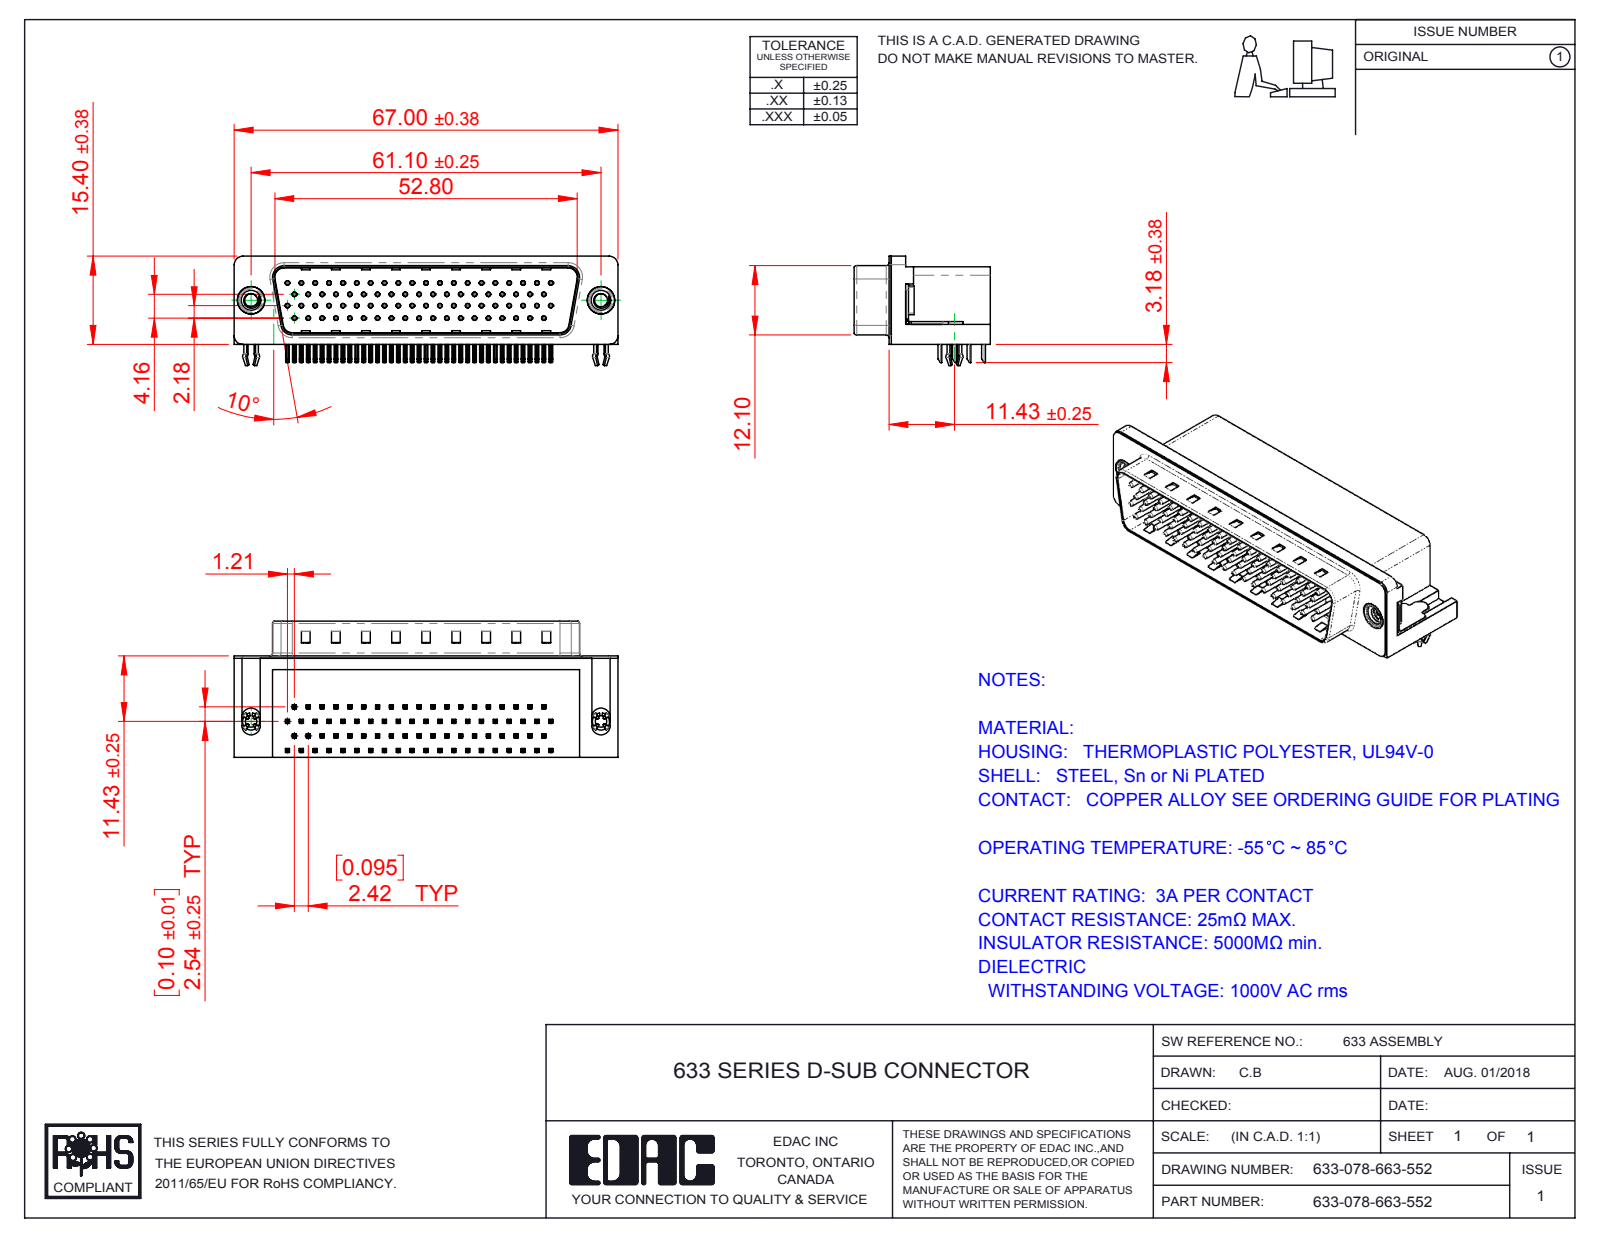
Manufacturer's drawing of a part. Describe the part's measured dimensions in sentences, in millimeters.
The part is named "633 Contact Top 78; 633-078-663-552; 633 4-40 Threaded Rivet; 633 4 Prong Board Lock_78 Contact (+5 more)". Its 3-D file was written by "SolidWorks 2016 (CONFIG_CONTROL_DESIGN)". It is 84 solids with 6396 faces: 4023 planar, 1784 cylindrical and 589 other. Overall it measures 67 by 23.8 by 19.1 millimeters. Its volume is 14 624 cubic millimeters and its surface area 16 429 square millimeters. Round holes: 78 of diameter 0.35, 78 of diameter 0.8, 2 of diameter 2, 2 of diameter 2.26, 2 of diameter 4, 2 of diameter 4.8, 2 of diameter 5. Round bosses or shafts: 78 of diameter 0.75, 2 of diameter 4.9, 2 of diameter 4.75, 2 of diameter 3.9, 2 of diameter 3. Partial cylindrical surfaces (rounded edges, fillets, slot ends): 324 of radius 0.25, 156 of radius 0.12, 16 of radius 1, 9 of radius 0.5, 8 of radius 1.6, 6 of radius 1.5, 4 of radius 0.45, 4 of radius 0.9. The main face-to-face distances are 0.4, 13.2, 17.3, 11.7, 13.35, 2.05, 13.75, 1.65, 1.85, 11.9. The hole center spacings are 2.42, 4.84, 7.26, 9.68, 6.26, 7.13, 12.1, 8.62.
